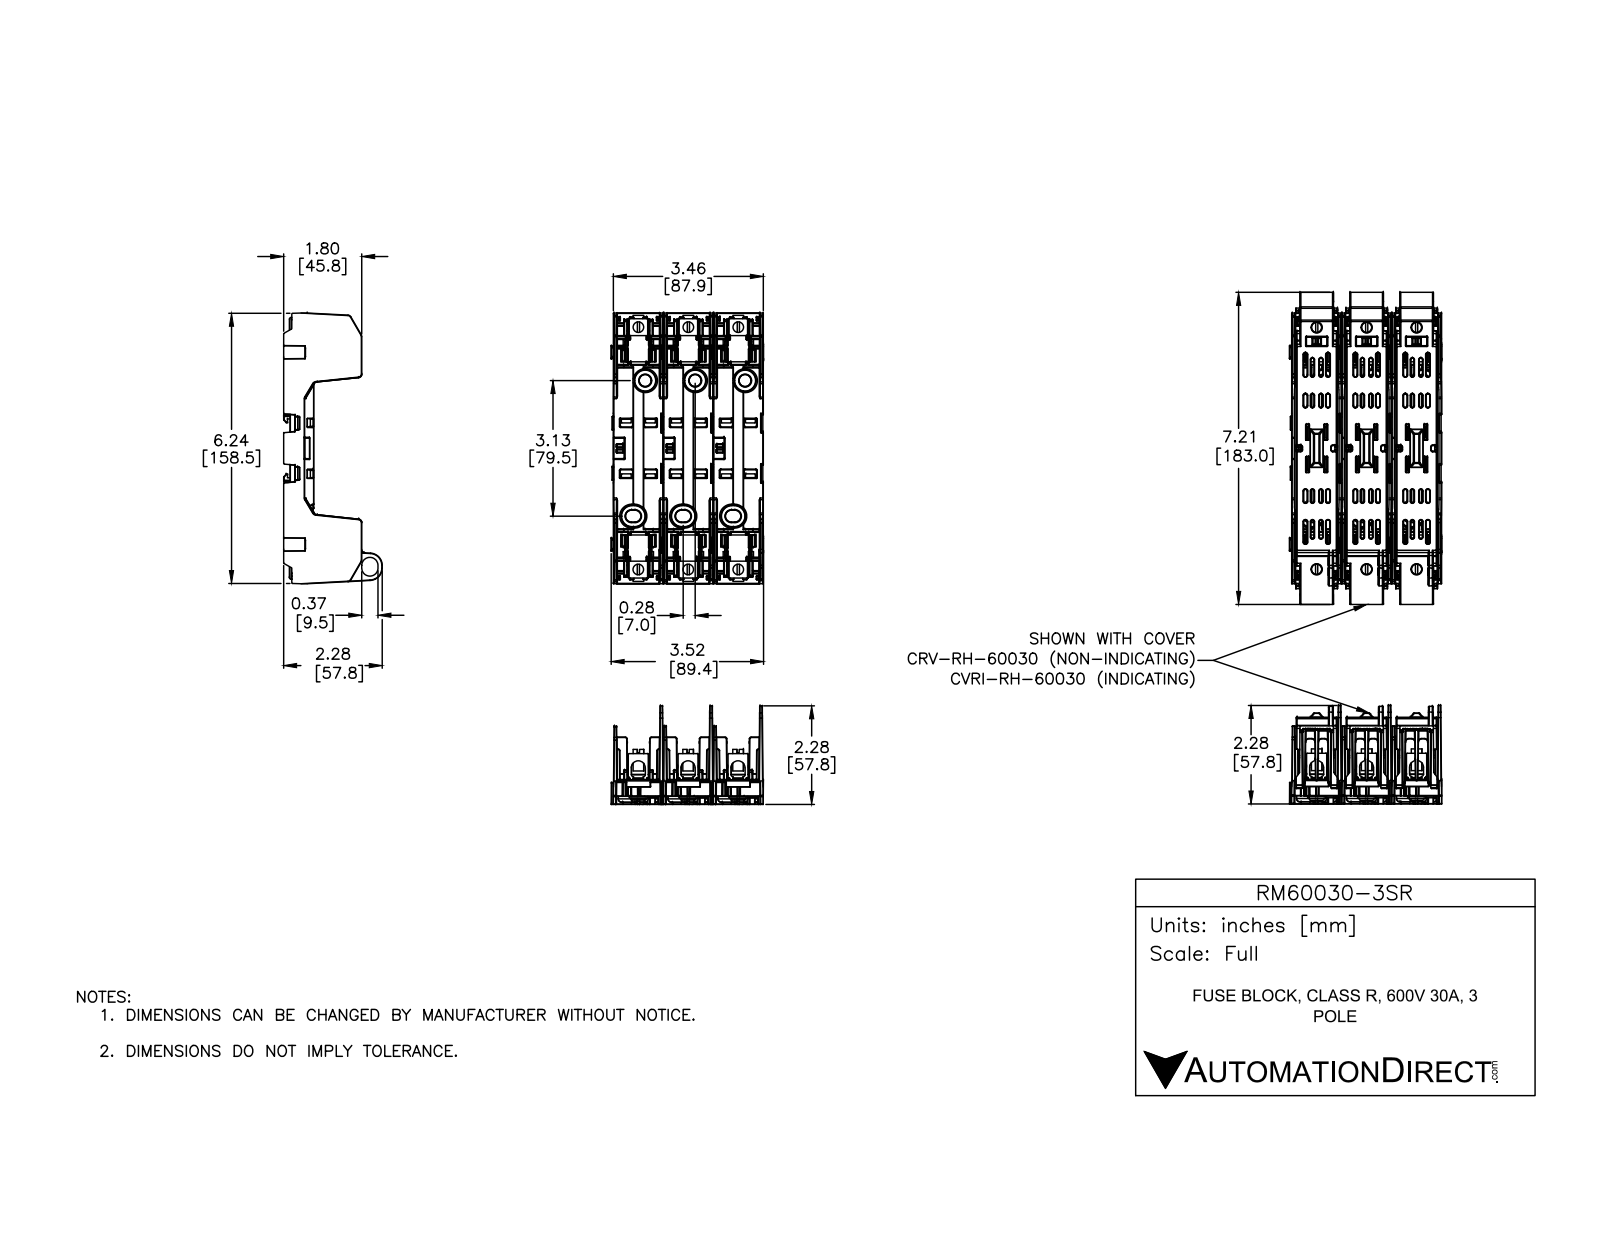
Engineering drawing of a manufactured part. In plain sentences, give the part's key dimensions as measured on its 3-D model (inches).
The part is named "RM60030-1SR; RM60030-3SR". Its 3-D file was written by "SolidWorks 2018 (AUTOMOTIVE_DESIGN)". It is 21 solids with 10545 faces: 2370 planar, 4419 cylindrical and 3756 other. Overall it measures 6.254 by 3.527 by 2.276 inches. Its volume is 9.551 cubic inches and its surface area 192.5 square inches. Round holes: 6 of diameter 0.244. Round bosses or shafts: 6 of diameter 0.244. Partial cylindrical surfaces (rounded edges, fillets, slot ends): 1263 of radius 0.01, 950 of radius 0.006, 159 of radius 0.02, 121 of radius 0.039, 48 of radius 0.02, 47 of radius 0.079, 26 of radius 0.075, 18 of radius 0.059. The main face-to-face distances are 1.157, 1.067, 1.158, 2.315, 2.315, 2.224, 0.091, 0.384, 0.187, 0.065. The hole center spacings are 1.157, 5.597, 5.715, 1.158, 2.315, 2.315, 5.716, 5.716.
